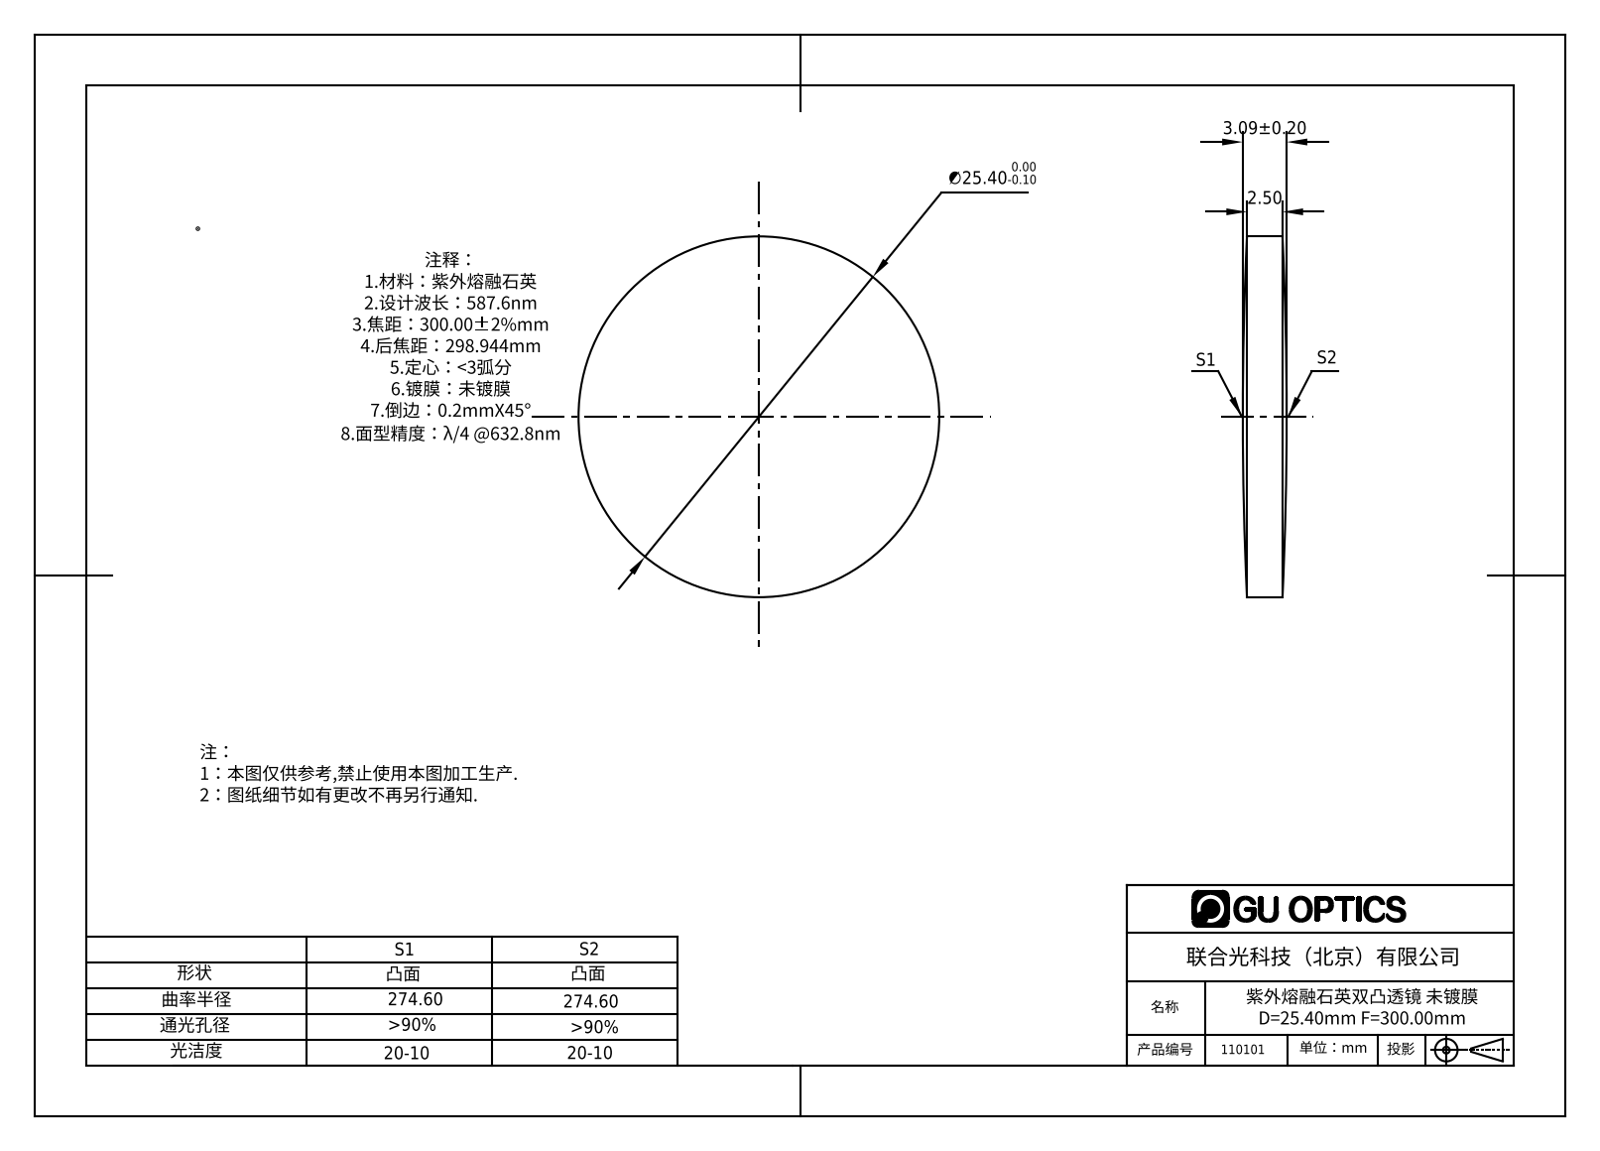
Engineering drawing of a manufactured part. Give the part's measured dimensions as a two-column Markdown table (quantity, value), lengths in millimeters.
| quantity | value |
| --- | --- |
| part name | 110101 |
| STEP written by | SolidWorks 2016 (CONFIG_CONTROL_DESIGN) |
| units | millimeters |
| bodies | 1 solid, 6 faces (0 planar, 2 cylindrical, 4 other) |
| overall size | 25.4 × 25.4 × 3.09 |
| volume | 1 416 mm³ |
| surface area | 1 213 mm² |
| round bosses / shafts (diameter × count) | 25.4 × 1 |
